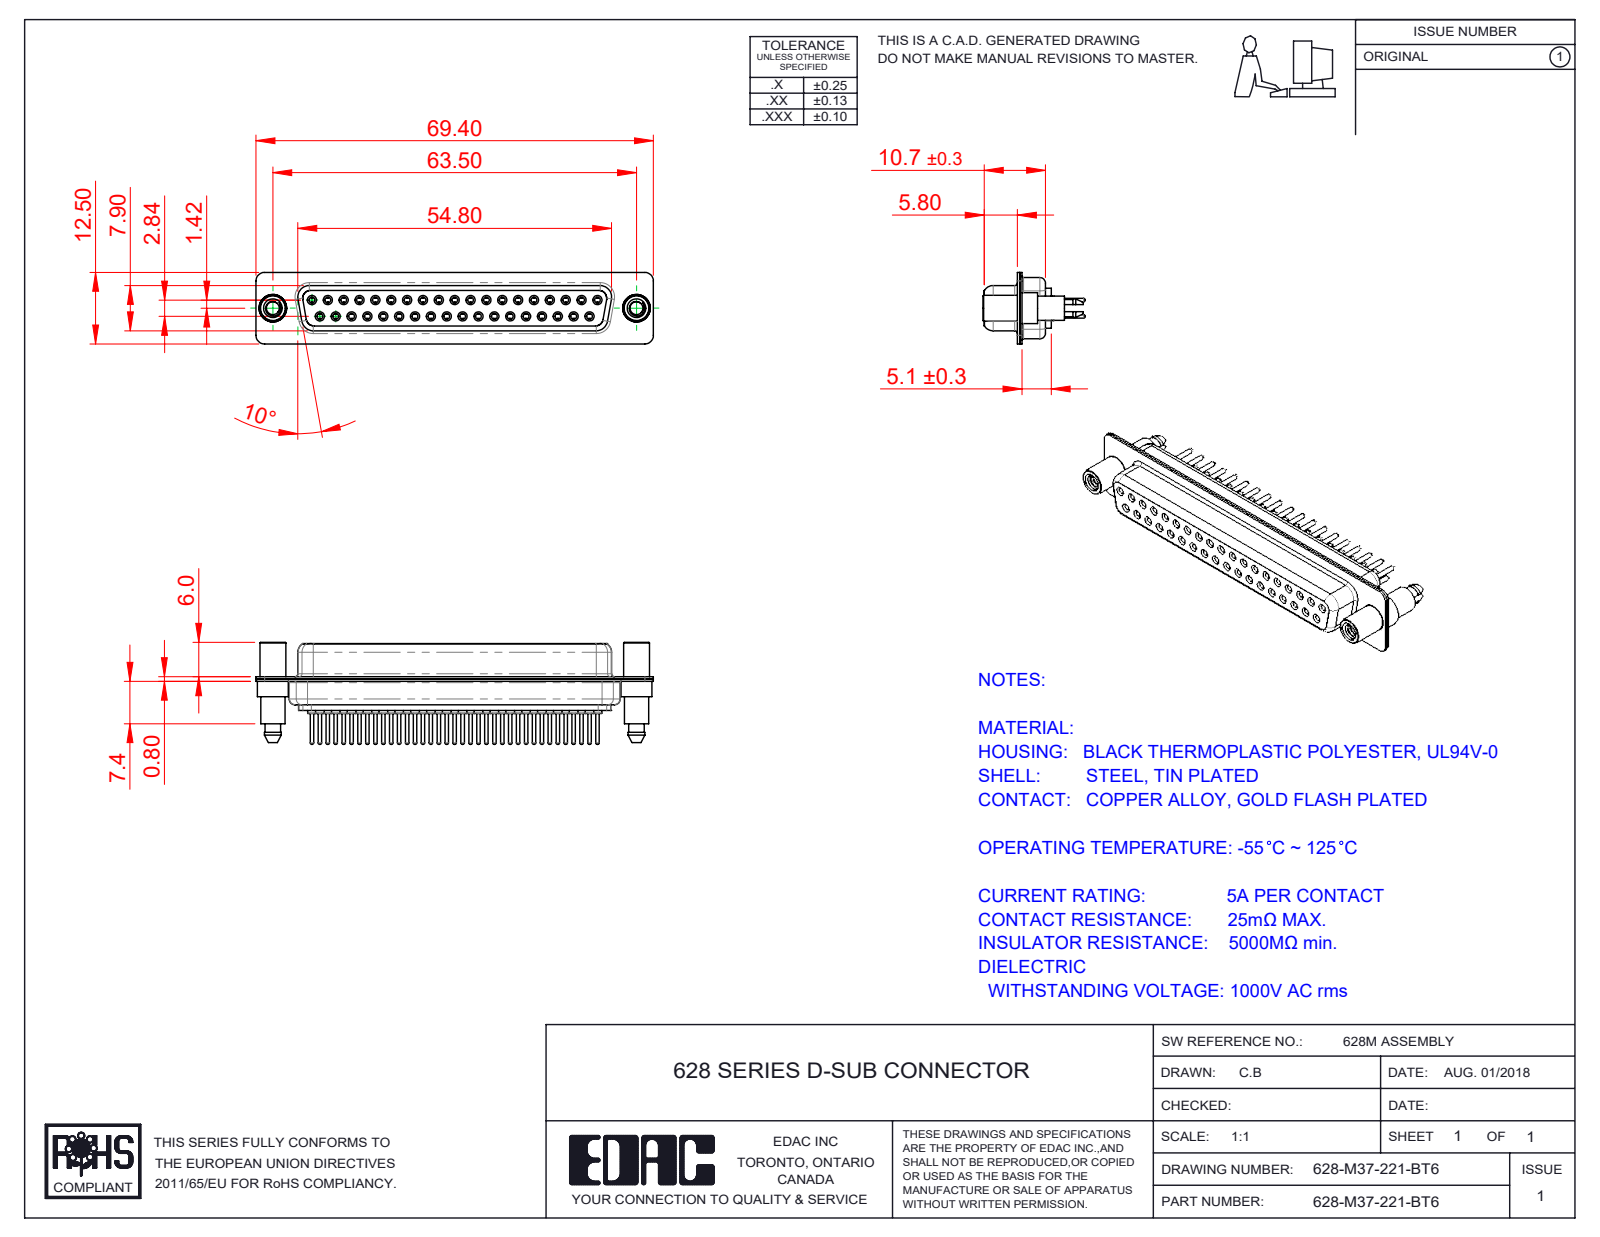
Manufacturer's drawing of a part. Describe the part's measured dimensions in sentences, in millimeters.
The part is named "628M Contact Row 1_21; 628-M37-221-BT6; 628M Shell Rear_37 Contacts; 628M Contact Row 2_21 (+3 more)". Its 3-D file was written by "SolidWorks 2020 (CONFIG_CONTROL_DESIGN)". It is 42 solids with 2366 faces: 640 planar, 868 cylindrical and 858 other. Overall it measures 69.4 by 17.8 by 12.5 millimeters. Its volume is 5 592 cubic millimeters and its surface area 13 134 square millimeters. Round holes: 37 of diameter 1, 37 of diameter 1.1, 37 of diameter 1.7, 37 of diameter 1.8, 37 of diameter 2, 2 of diameter 2.26, 2 of diameter 4, 2 of diameter 4.8. Round bosses or shafts: 37 of diameter 2.2, 37 of diameter 1.6, 37 of diameter 1.5, 37 of diameter 0.6, 2 of diameter 5.4, 2 of diameter 4.9, 2 of diameter 4.5, 2 of diameter 4.25. Partial cylindrical surfaces (rounded edges, fillets, slot ends): 18 of radius 1.5, 12 of radius 2, 10 of radius 1.6, 8 of radius 1.35, 4 of radius 0.25, 4 of radius 0.5, 4 of radius 0.6, 4 of radius 0.65. The main face-to-face distances are 0.4, 1.4, 0.45, 8.45, 8.9, 1.8, 6.2, 7.05, 1, 1.85. The hole center spacings are 2.77, 5.54, 8.31, 3.16, 11.08, 13.85, 16.62, 19.39.
